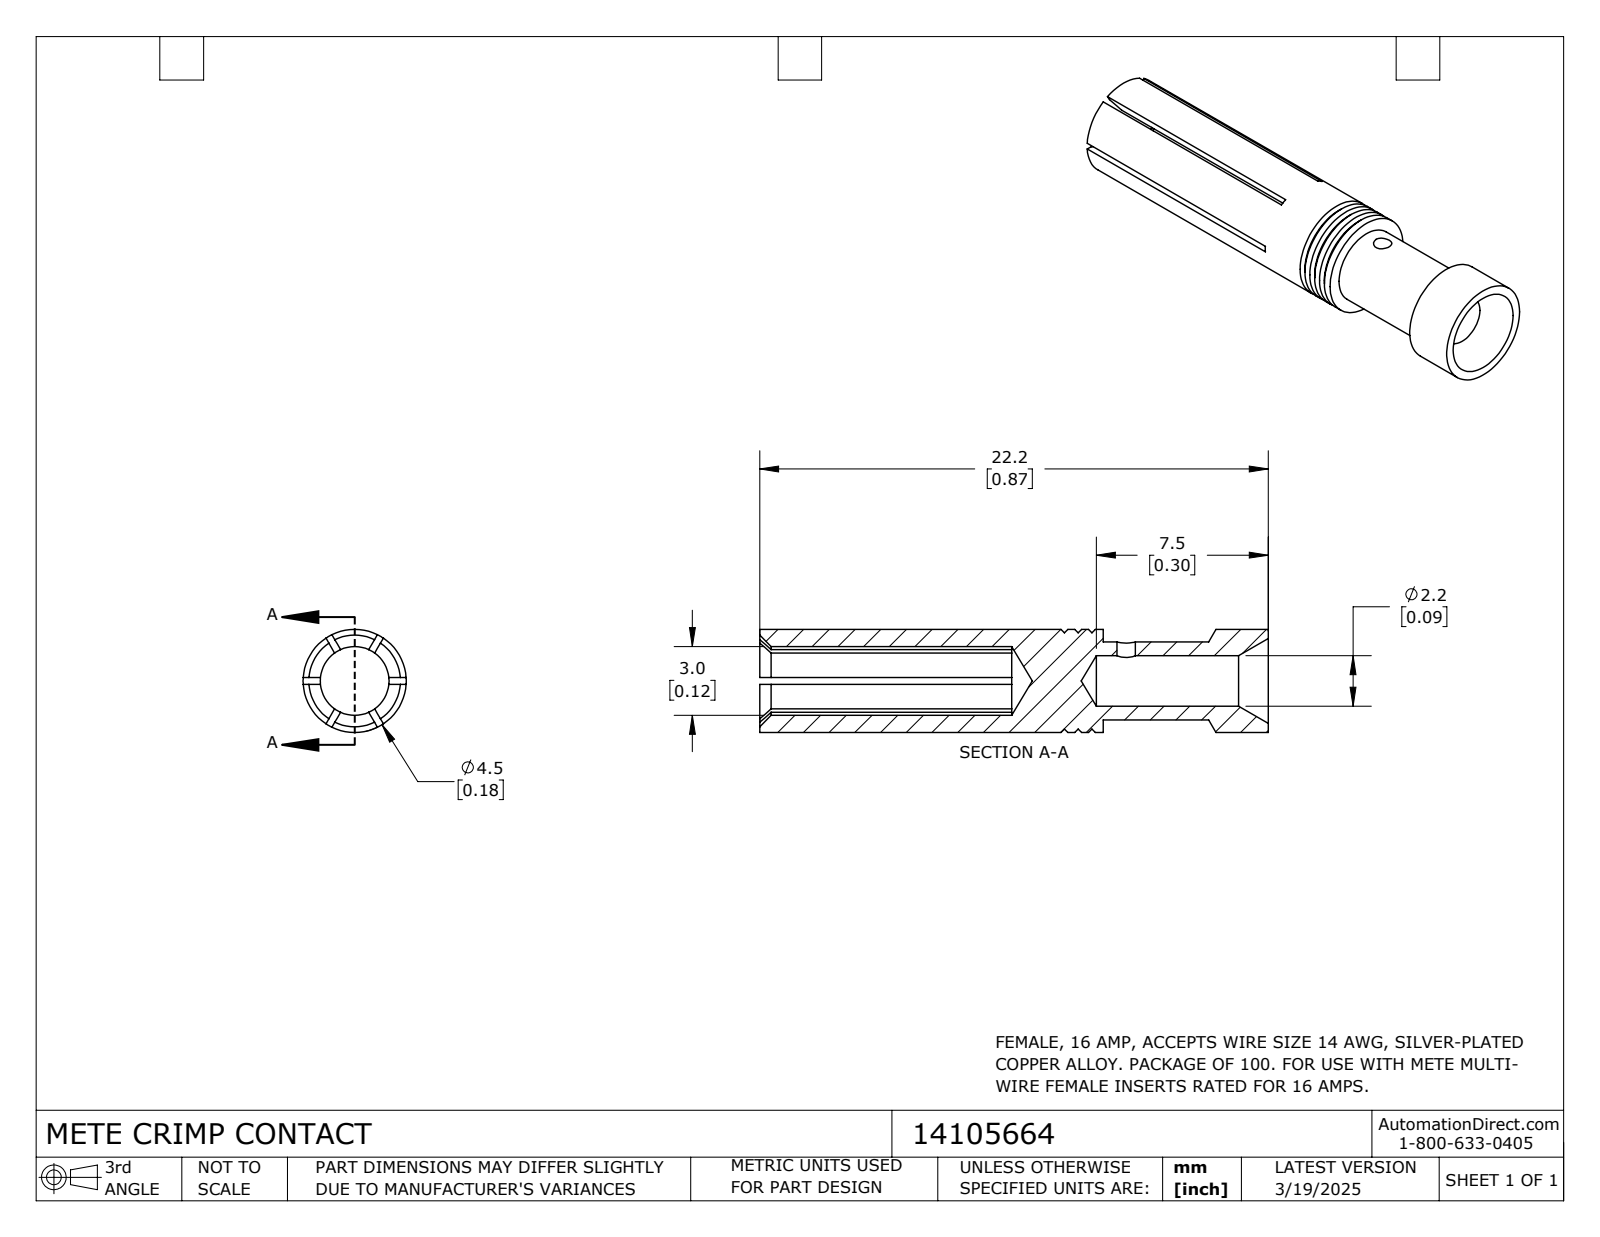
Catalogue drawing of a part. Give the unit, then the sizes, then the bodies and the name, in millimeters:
Units: millimetres
Overall size (bounding box): 22.2 × 4.5 × 4.5
Round holes (diameter × count): ⌀0.8 ×1, ⌀2.2 ×1, ⌀3 ×1
Round bosses / shafts (diameter × count): ⌀4.5 ×1, ⌀3.4 ×1
Main face-to-face distances: 7.2, 22.2, 15, 11.2, 4, 11
Volume: 190 mm³ · Surface area: 557 mm²
Bodies: 1 solid, 74 faces (26 planar, 22 cylindrical, 26 other)
Part name (STEP PRODUCT): 14105664
STEP written by: SolidWorks 2024 (CONFIG_CONTROL_DESIGN)
